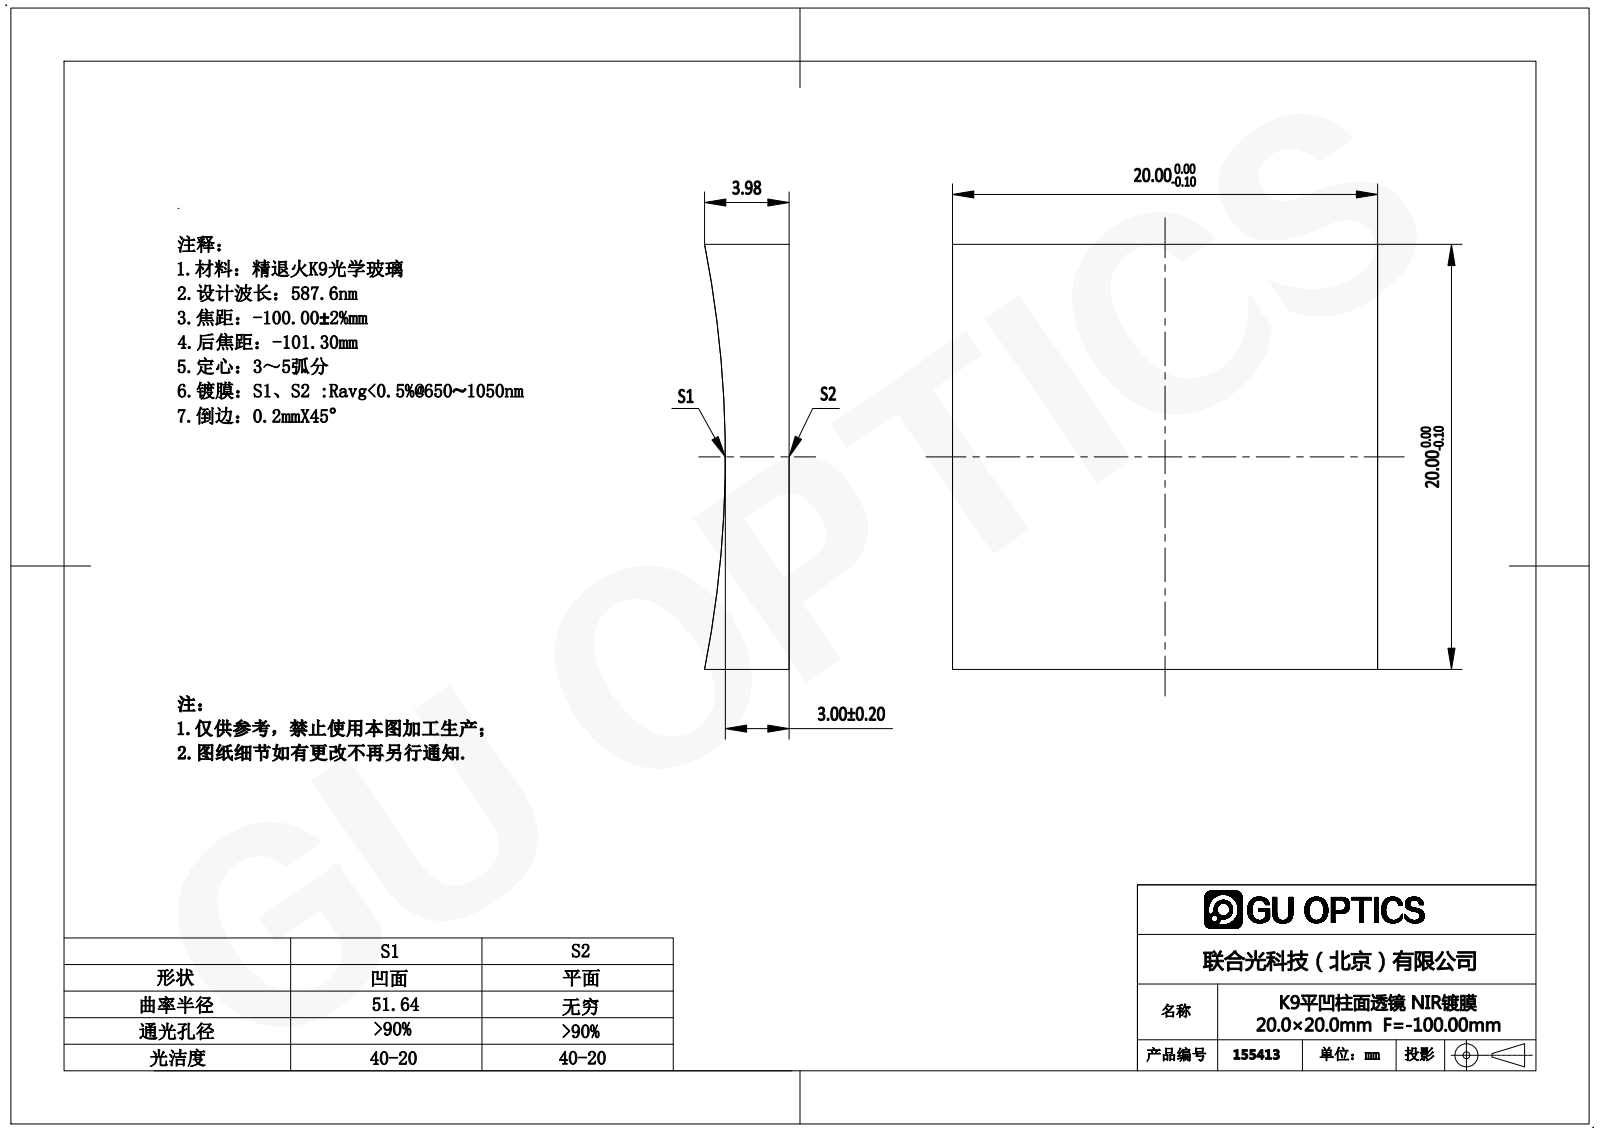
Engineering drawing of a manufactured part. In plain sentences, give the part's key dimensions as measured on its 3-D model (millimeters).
The part is named "155347". Its 3-D file was written by "SolidWorks 2016 (AUTOMOTIVE_DESIGN)". It is 1 solid with 6 faces: 5 planar, 1 cylindrical and 0 other. Overall it measures 20 by 20 by 3.98 millimeters. Its volume is 1 330 cubic millimeters and its surface area 1 095 square millimeters. Partial cylindrical surfaces (rounded edges, fillets, slot ends): 1 of radius 51.64. The main face-to-face distances are 20.
